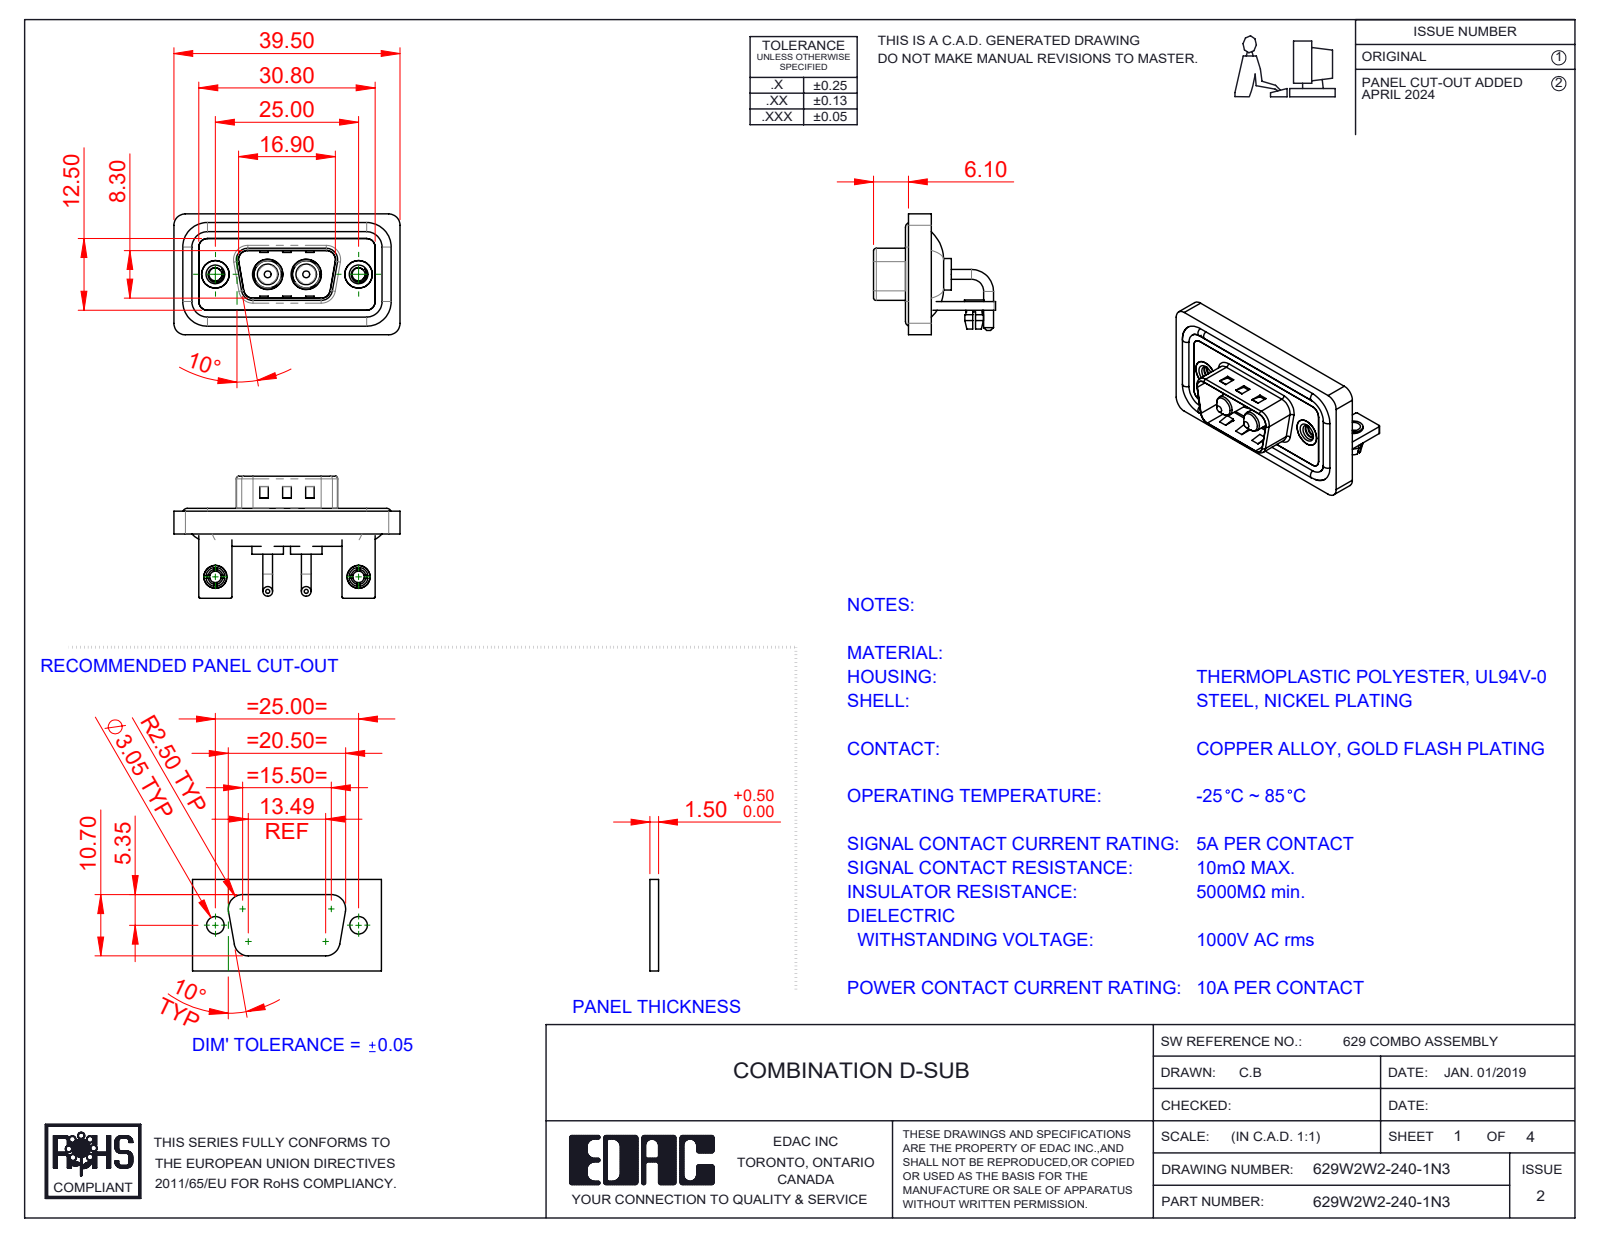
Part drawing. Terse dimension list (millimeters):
name: 629Combo Housing_2W2; 629Combo Waterproof Housing_09 Contacts; 629W2W2-140-1N3; 629Combo Threaded Rivet_3 (+5 more)
written by: SolidWorks 2023 (CONFIG_CONTROL_DESIGN)
unit: mm
bodies: 15 solids, 629 faces (233 planar, 272 cylindrical, 124 other)
size: 39.5 × 21.3 × 21.1
volume: 4 782 mm³; area: 7 863 mm²
holes: 2× ⌀2, 2× ⌀2.26, 2× ⌀2.5, 2× ⌀3.2, 2× ⌀4, 2× ⌀4.8, 2× ⌀4.85, 2× ⌀5, 2× ⌀5.3
bosses: 4× ⌀1.7, 4× ⌀1.6, 2× ⌀5.5, 2× ⌀5.2, 2× ⌀4.9, 2× ⌀4.75, 2× ⌀4, 2× ⌀3.75
rounds: 19× R2, 18× R1.5, 16× R0.25, 9× R0.5, 8× R1.6, 4× R0.6, 4× R0.65, 4× R0.9
face distances: 0.4, 1.5, 2.9, 0.8, 1.1, 1.2, 2.1, 1.6, 3.7, 2.5
hole spacings: 9.14, 15.86, 25, 6.72
